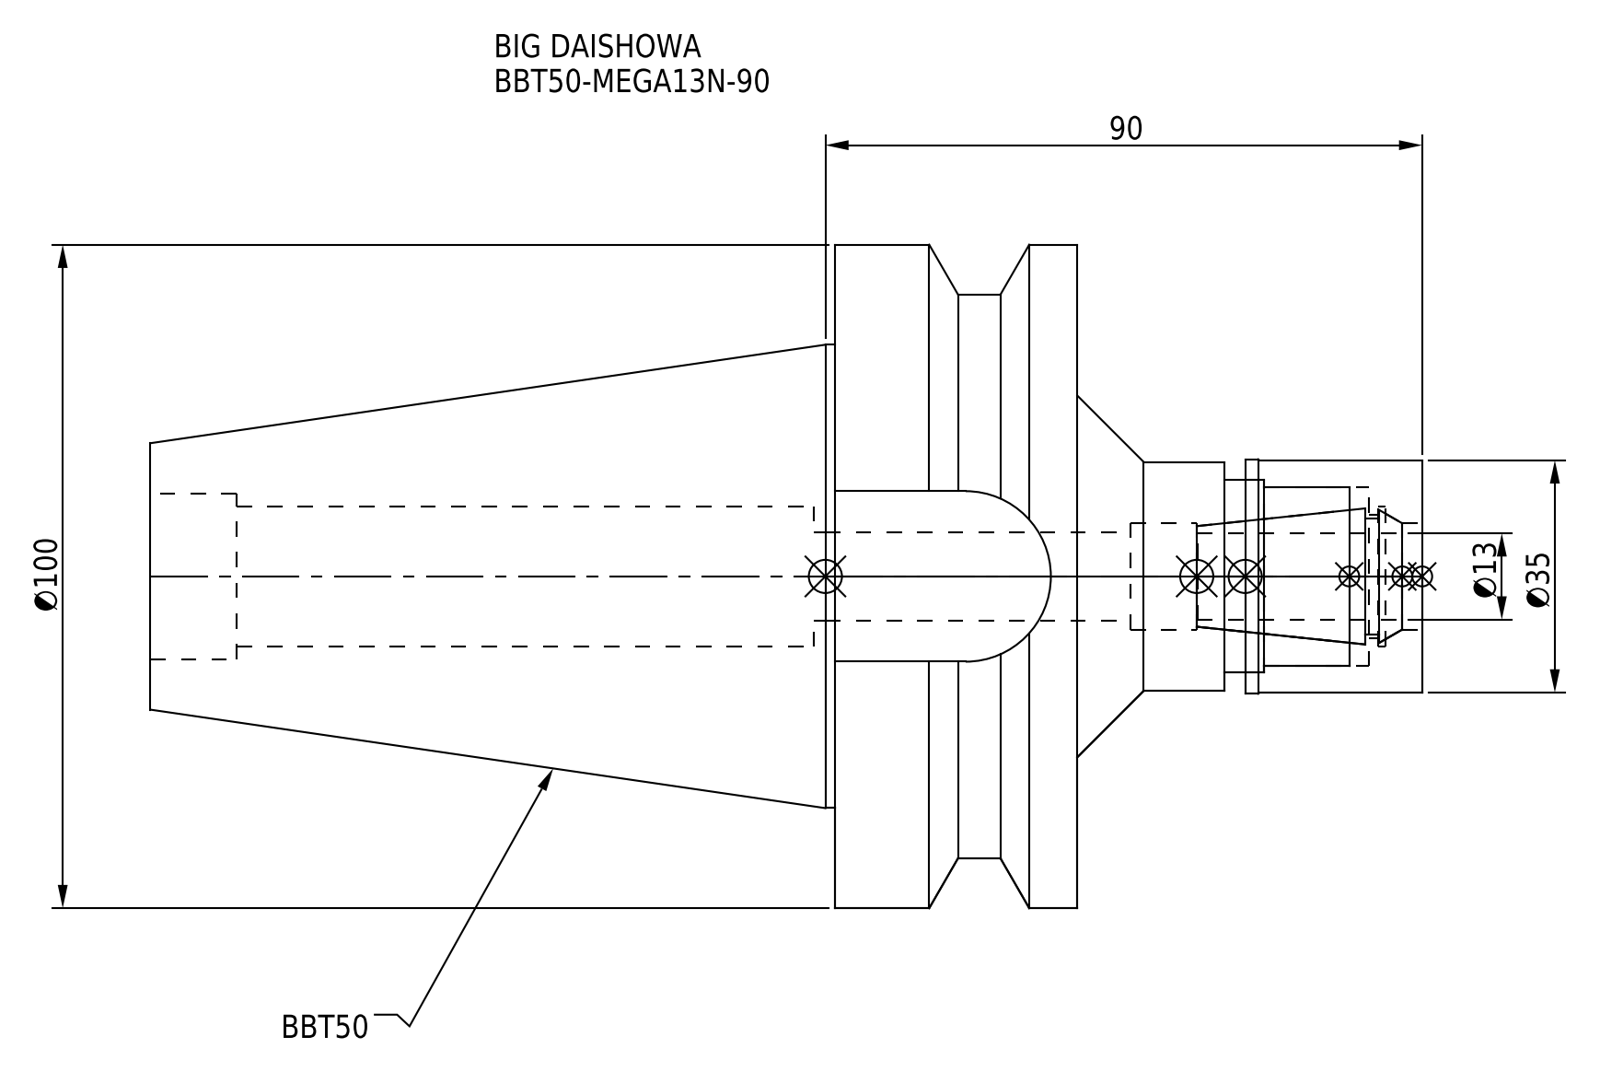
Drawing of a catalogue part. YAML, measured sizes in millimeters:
part_name: "BBT50-MEGA13N-90-130.stp; DXF_TEMP_ASSY_ASM_4_ASM.stp; BBT50MN13090-130_ASM.stp; BBT50-MEGA13N-90-130-FreeParts (+3 more)"
step_written_by: "SolidWorks 2019 (CONFIG_CONTROL_DESIGN)"
units: millimeters
bodies: {solids: 2, faces: 76, planar: 22, cylindrical: 40, other: 14}
overall_size: [191.8, 100, 100]
volume: 498924
surface_area: 65738
round_holes:
  - {diameter: 13.3, count: 1}
  - {diameter: 16, count: 1}
  - {diameter: 18.5, count: 1}
  - {diameter: 21, count: 1}
  - {diameter: 21.2, count: 1}
  - {diameter: 25, count: 1}
  - {diameter: 27, count: 1}
  - {diameter: 29, count: 1}
round_bosses_or_shafts:
  - {diameter: 100, count: 1}
  - {diameter: 85, count: 1}
  - {diameter: 69.85, count: 1}
  - {diameter: 35.3, count: 1}
  - {diameter: 35, count: 1}
  - {diameter: 34.5, count: 1}
partial_cylinders:
  - {radius: 12.85, count: 1}
face_to_face_distances: [36.5, 139.8, 103.3, 70.8, 52, 88.5, 191.8, 25.7, 8, 44]
